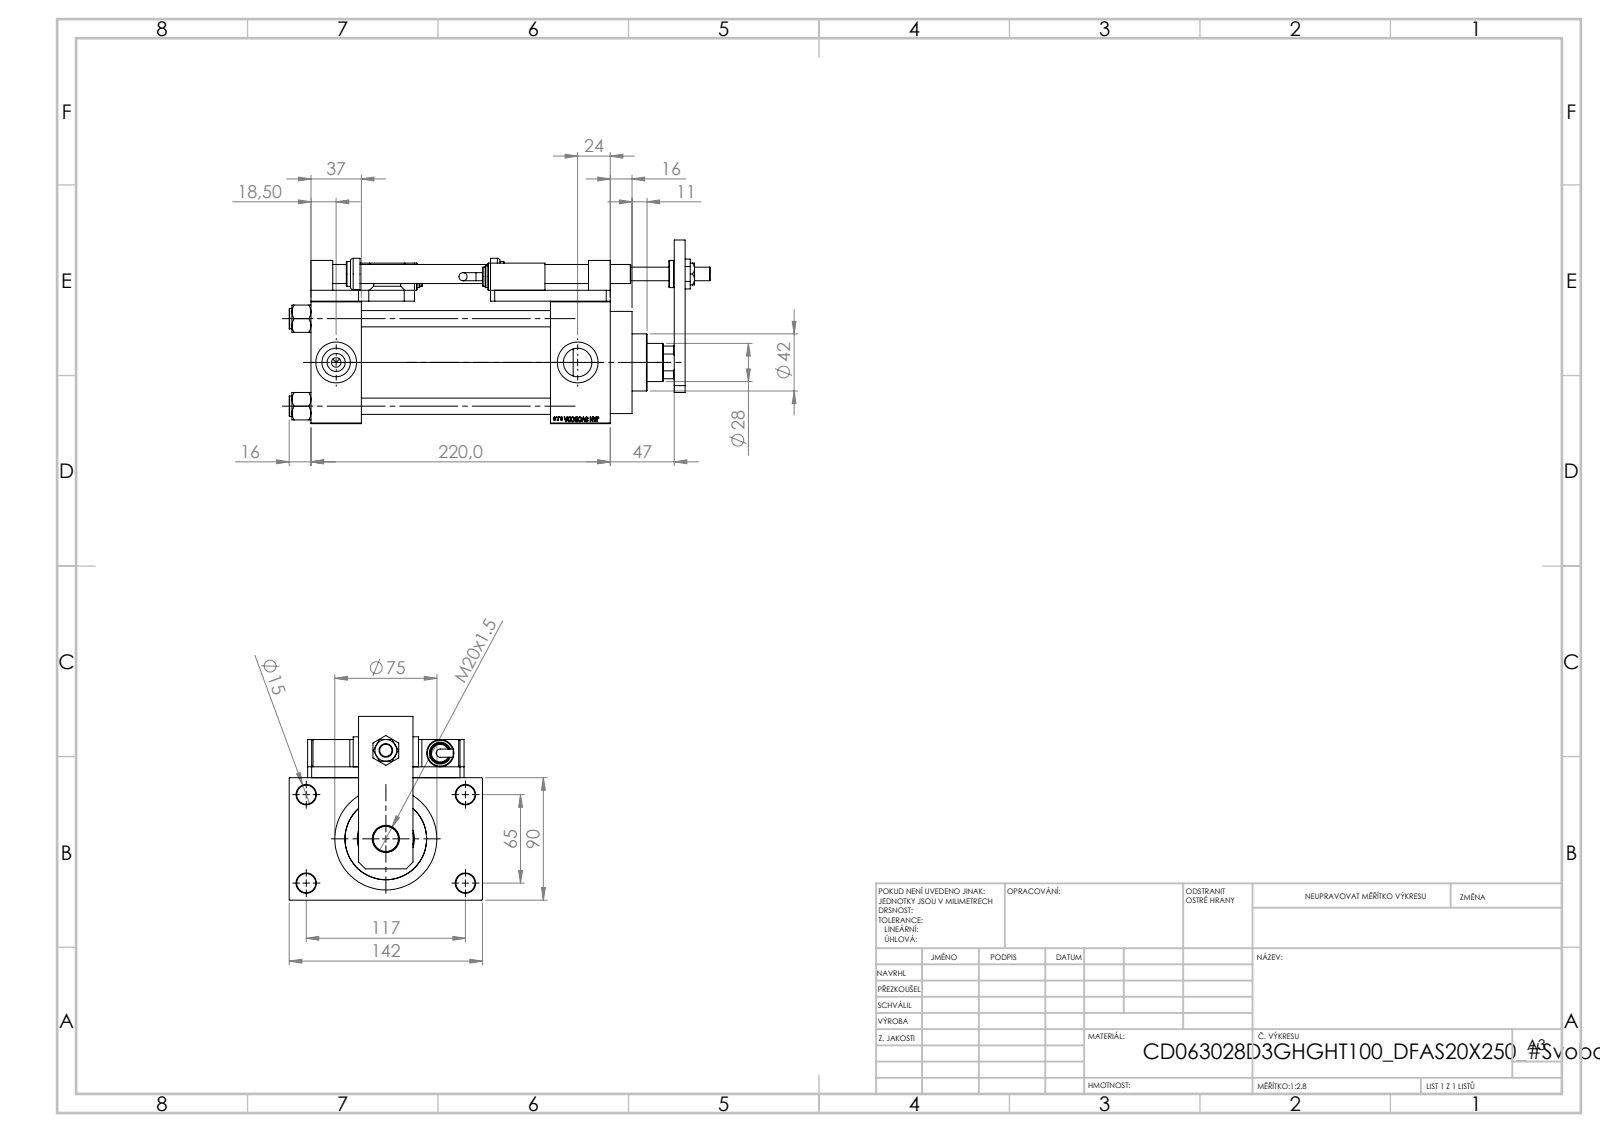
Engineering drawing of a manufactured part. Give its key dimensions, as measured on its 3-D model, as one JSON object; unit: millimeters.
{"part_name": "V215CD_D_Body; V215CD_SWITCH_Q_PODLOZKA_BACK; Zatka_pro_OIL_PORT; V215CD_VC_A (+8 more)", "step_written_by": "SolidWorks 2019 (CONFIG_CONTROL_DESIGN)", "units": "millimeters", "bodies": {"solids": 26, "faces": 1432, "planar": 666, "cylindrical": 167, "other": 599}, "overall_size": [309.5, 142, 135], "volume_mm3": 1504000, "surface_area_mm2": 345977, "round_holes": [[14, 5], [8.5, 4], [12, 4], [13.5, 4], [20.96, 4], [30, 4], [7, 3], [10, 1], [18.5, 1], [20, 1], [28, 1], [31, 1]], "round_bosses_or_shafts": [[15, 4], [20, 3], [16, 2], [14, 2], [6, 2], [75, 1], [69, 1], [42, 1]], "partial_cylinders_radius": [[7.5, 4], [13.5, 1]], "face_to_face_distances": [8, 90, 44, 220, 37, 98, 183, 176, 139, 47], "hole_center_spacings": [66.92, 26.35, 45.47, 64.3, 69.81, 90.65, 111.34, 65]}
